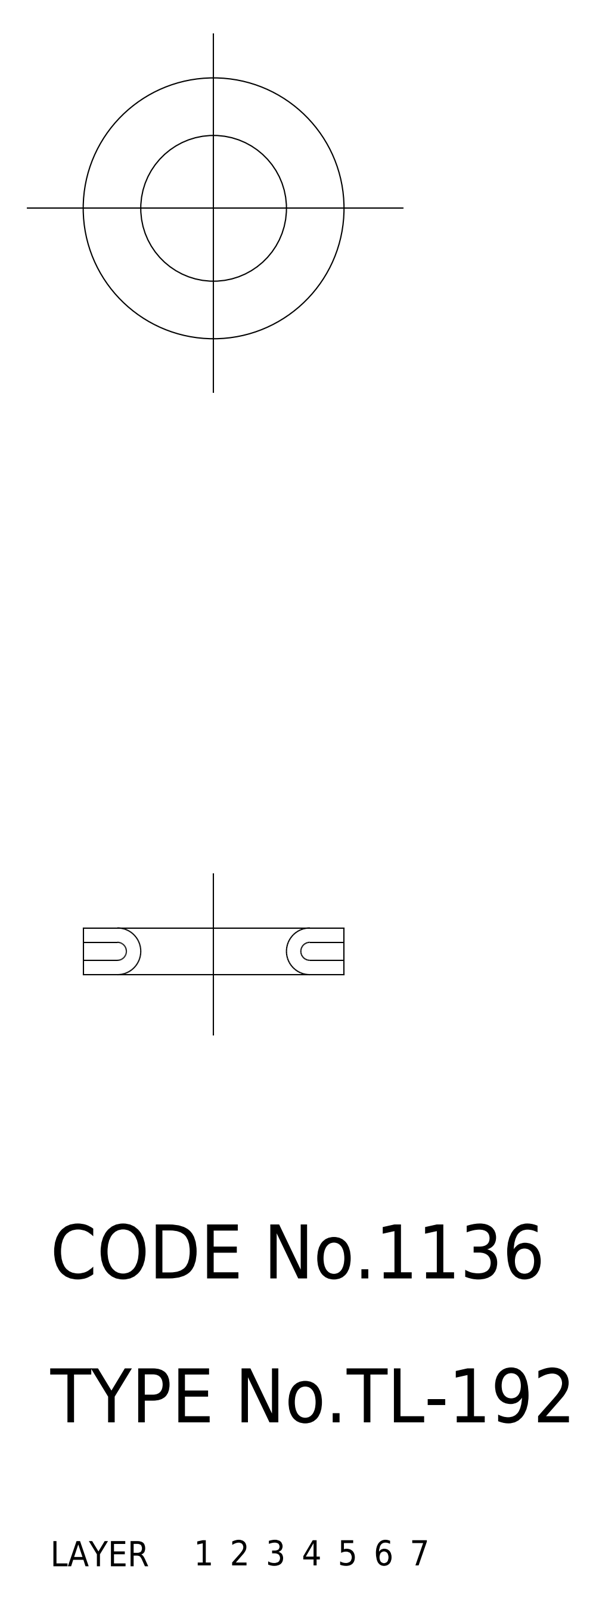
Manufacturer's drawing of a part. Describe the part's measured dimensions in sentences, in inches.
The part is named "grommet". Its 3-D file was written by "CADfix (AUTOMOTIVE_DESIGN)". It is 1 solid with 12 faces: 0 planar, 0 cylindrical and 12 other. Overall it measures 0.571 by 0.571 by 0.102 inches. Its volume is 0.011 cubic inches and its surface area 0.837 square inches.
